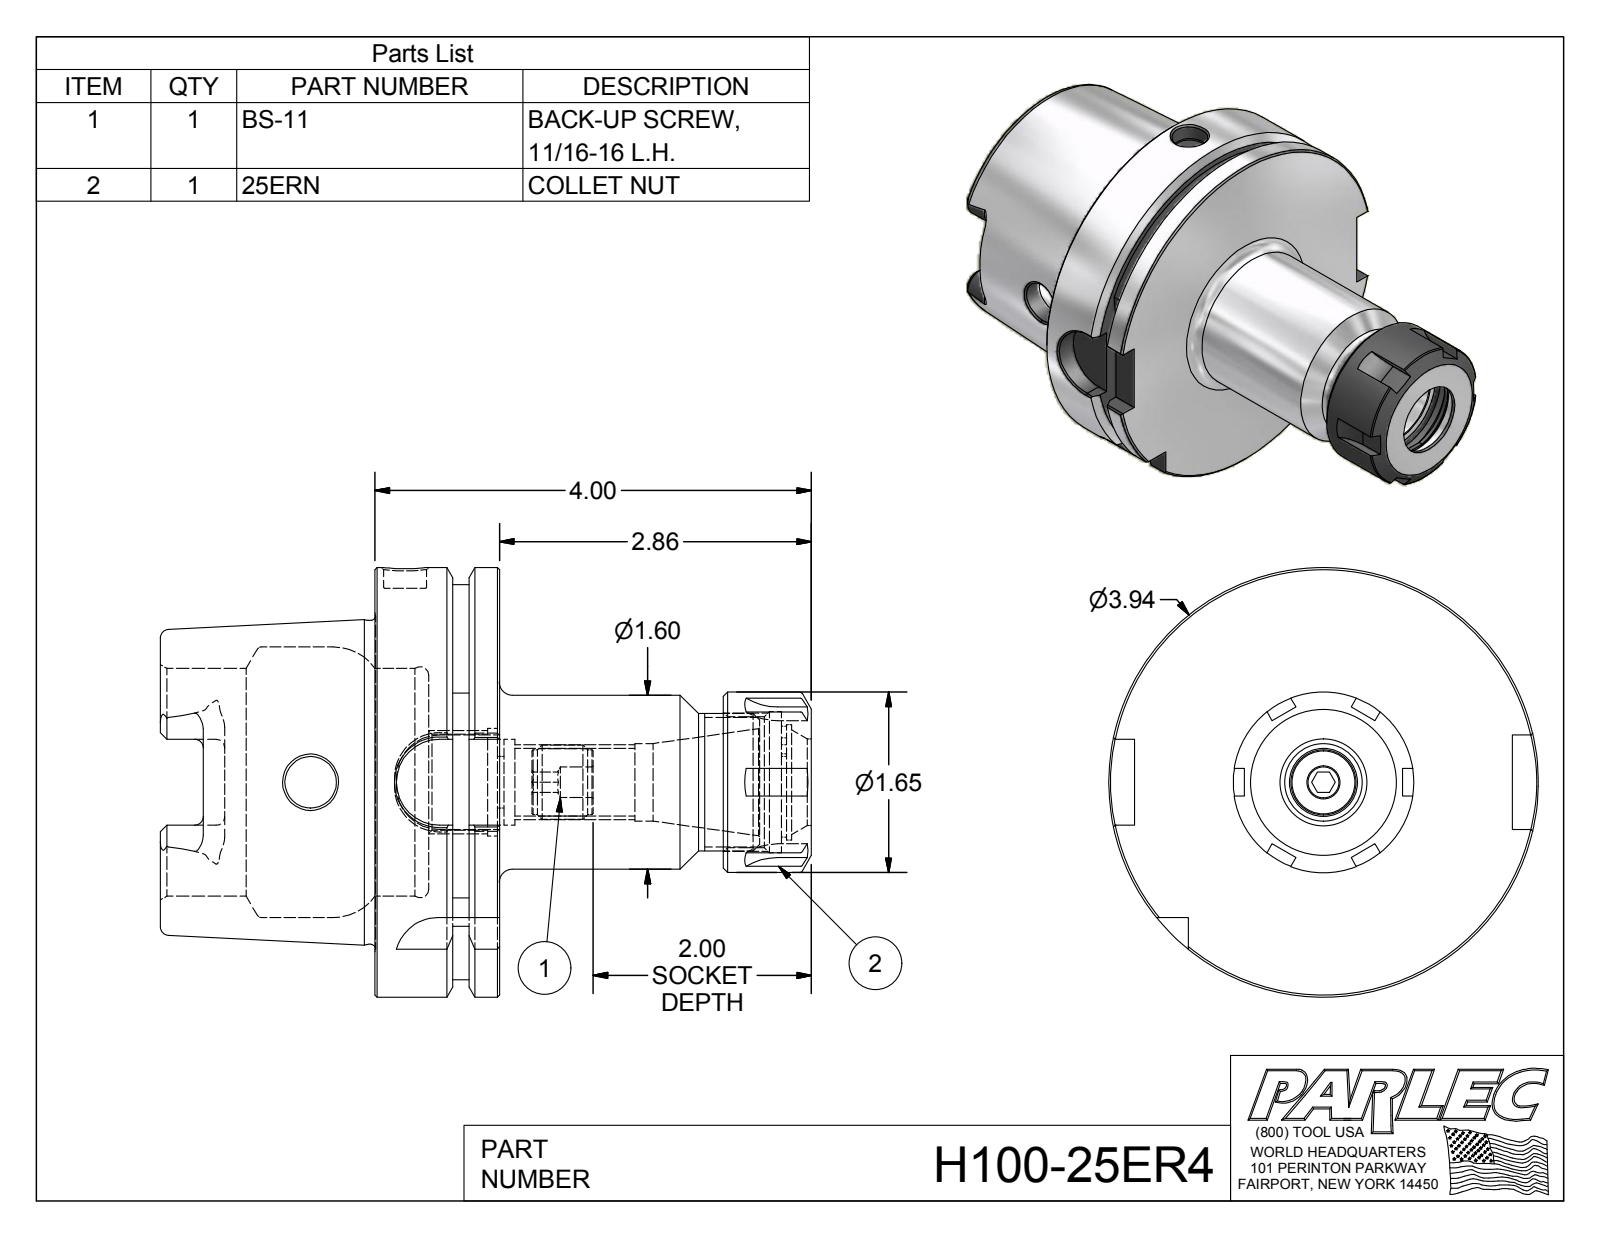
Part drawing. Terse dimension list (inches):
name: H100-25ER4; H100-25ER4-1; BS-11; 25ERN
written by: Autodesk Inventor 2012 (AUTOMOTIVE_DESIGN)
unit: in
bodies: 3 solids, 206 faces (82 planar, 57 cylindrical, 67 other)
size: 5.969 × 3.937 × 3.937
volume: 19.74 in³; area: 105.7 in²
holes: 2× ⌀0.472, 1× ⌀0.28, 1× ⌀0.394, 1× ⌀0.472, 1× ⌀0.62, 1× ⌀0.71, 1× ⌀0.785, 1× ⌀0.794, 1× ⌀0.881, 1× ⌀0.985, 1× ⌀1.057, 1× ⌀1.201
bosses: 1× ⌀3.937, 1× ⌀2.967, 1× ⌀1.654, 1× ⌀1.595, 1× ⌀1.26, 1× ⌀0.681, 1× ⌀0.595
rounds: 6× R0.079, 6× R0.5, 4× R0.192, 4× R0.394, 1× R0.472, 1× R0.515, 1× R1.811
face distances: 1.142, 0.492, 0.65, 1.969, 2.461, 3.11, 5.969, 4, 3.508, 2.858
